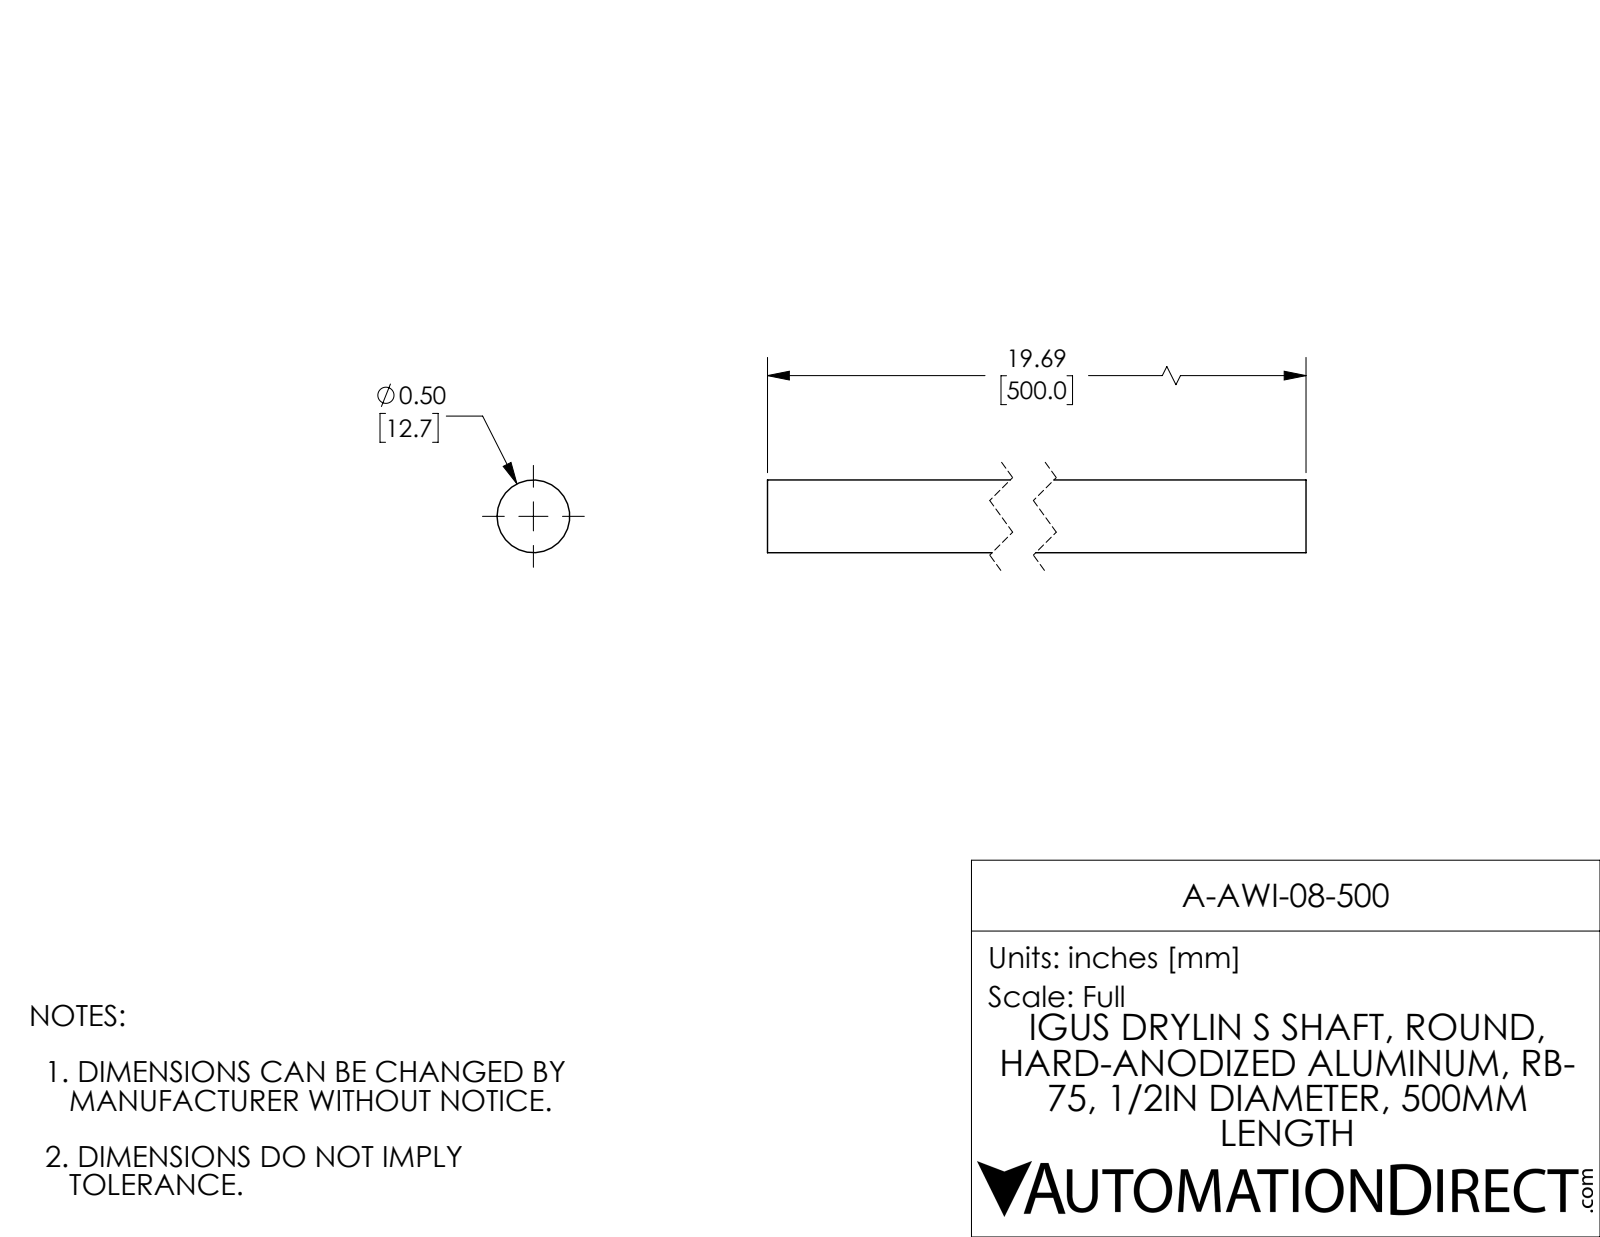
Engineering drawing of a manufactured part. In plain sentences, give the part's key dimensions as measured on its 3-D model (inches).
The part is named "A-AWI-08-500". Its 3-D file was written by "SolidWorks 2017 (AUTOMOTIVE_DESIGN)". It is 1 solid with 4 faces: 2 planar, 2 cylindrical and 0 other. Overall it measures 19.685 by 0.5 by 0.5 inches. Its volume is 3.865 cubic inches and its surface area 31.31 square inches. Round bosses or shafts: 1 of diameter 0.5. The main face-to-face distances are 19.685.
